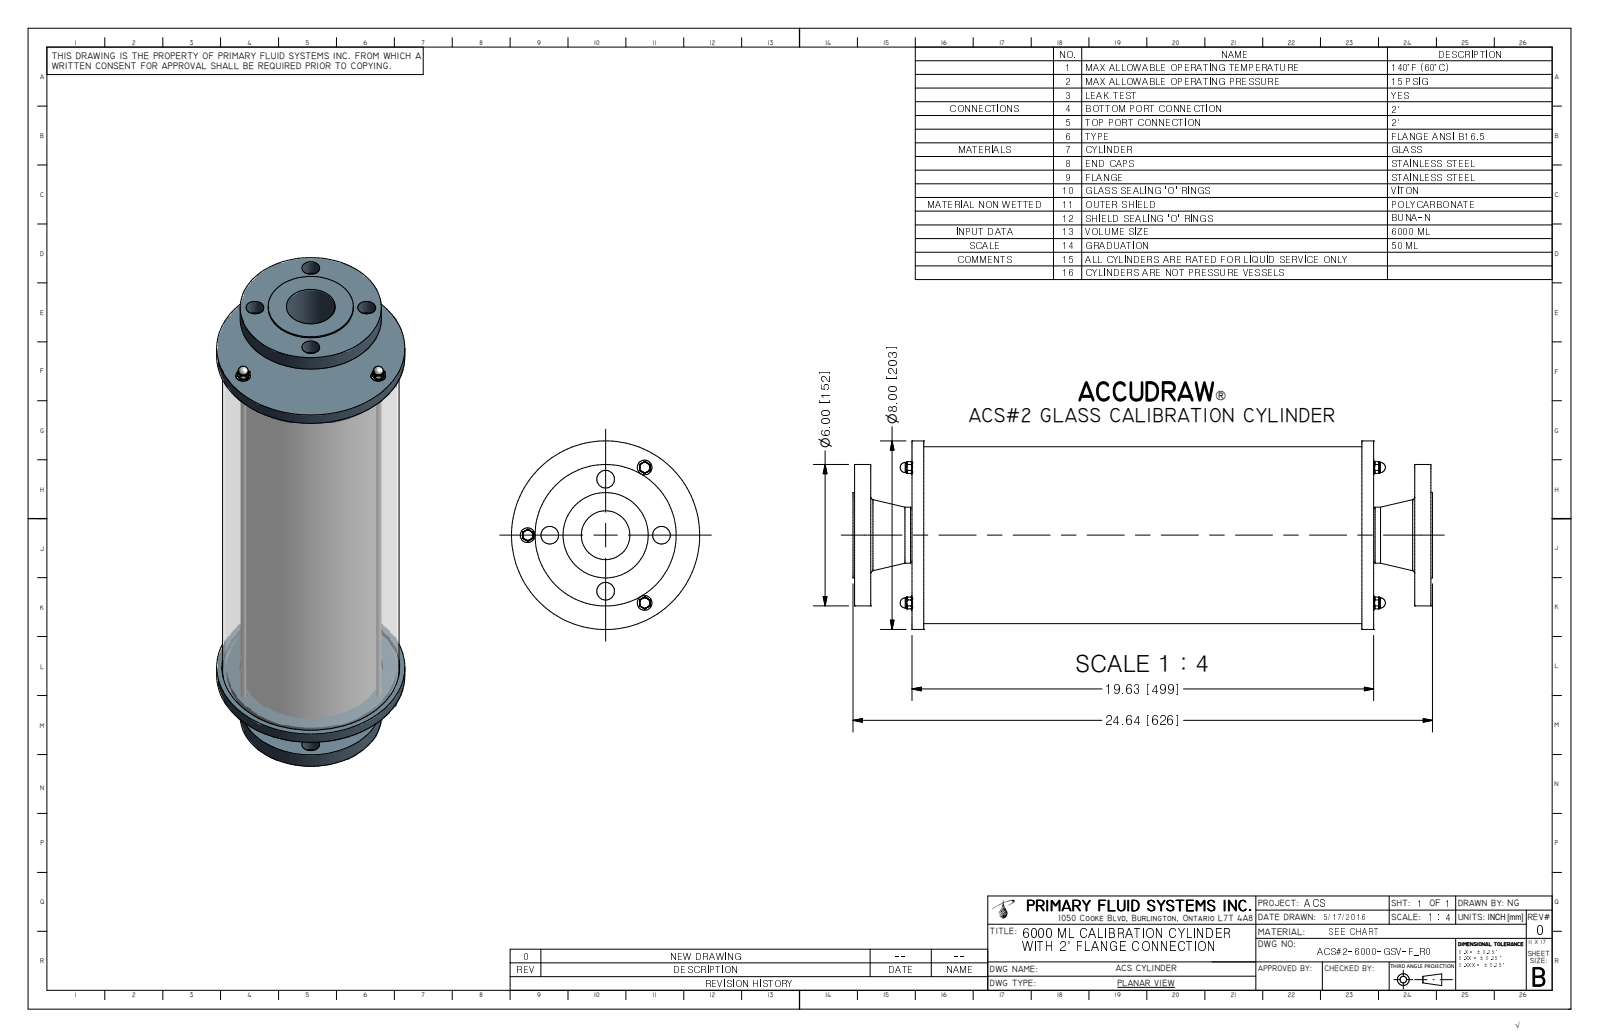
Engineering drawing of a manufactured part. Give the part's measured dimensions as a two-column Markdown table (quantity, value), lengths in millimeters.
| quantity | value |
| --- | --- |
| part name | ACS#2-6000-GSV-F_R0; ACS-3-6000-METAL-S_R1; ACS-2-6000_R6; ACS-1-6000-A_R0 (+4 more) |
| STEP written by | Autodesk Inventor 2009 (AUTOMOTIVE_DESIGN) |
| units | millimeters |
| bodies | 21 solids, 455 faces (46 planar, 57 cylindrical, 352 other) |
| overall size | 625.7 × 203.2 × 203.2 |
| volume | 3 368 000 mm³ |
| surface area | 1 353 000 mm² |
| round holes (diameter × count) | 19.1 × 4, 4.6 × 3, 6.8 × 3, 7.1 × 3, 52.5 × 1, 140 × 1, 154.1 × 1, 184.2 × 1, 191.8 × 1 |
| round bosses / shafts (diameter × count) | 15.9 × 3, 6.4 × 3, 203.2 × 1, 190.5 × 1, 182.9 × 1, 152.4 × 1, 150 × 1, 137.8 × 1 |
| main face-to-face distances | 498.6, 44.5, 543.1, 57.2, 530.4, 12.7, 485.9, 17.5, 62, 74.7 |
| hole center spacings | 60.3, 85.3, 84.3, 44, 75.2, 103.6, 120.7, 125.8 |
